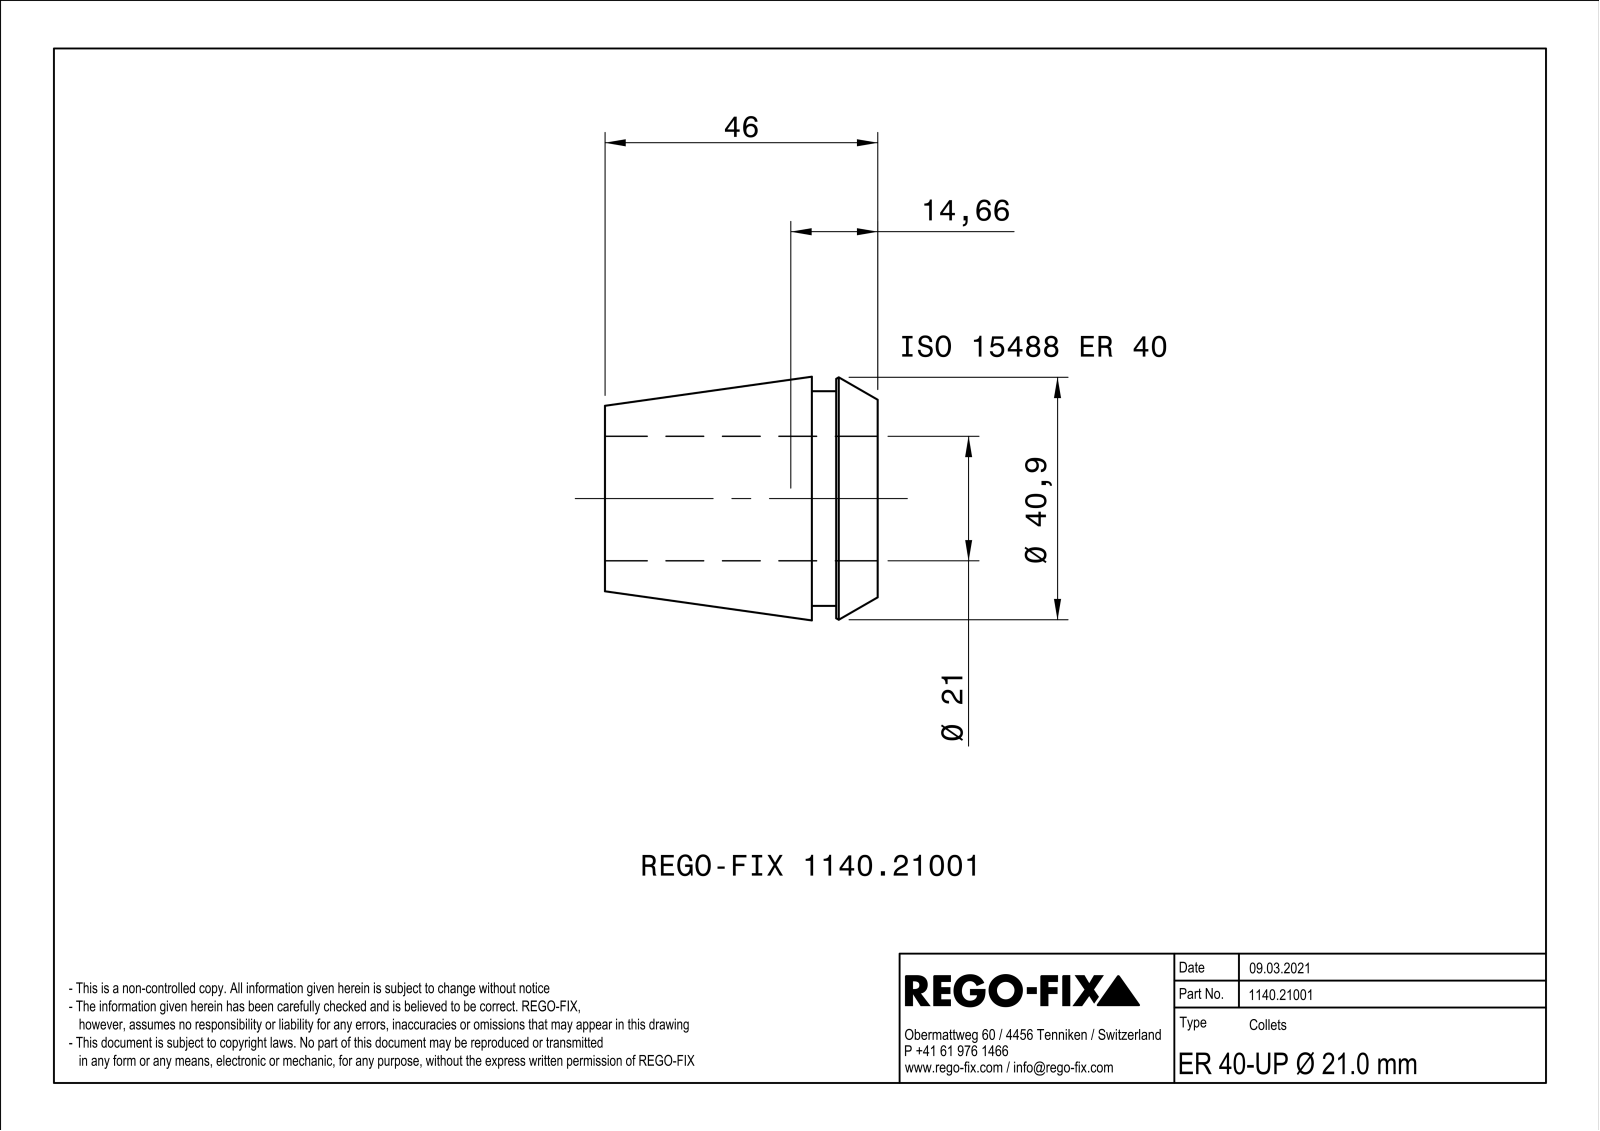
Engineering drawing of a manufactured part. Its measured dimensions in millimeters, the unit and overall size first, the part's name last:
Units: millimetres
Overall size (bounding box): 46 × 40.99 × 40.99
Round holes (diameter × count): ⌀21 ×1
Round bosses / shafts (diameter × count): ⌀36.2 ×1
Main face-to-face distances: 1, 46, 11.1, 34.9, 7, 4.1, 39, 7.5, 0.5, 3.6
Volume: 26 910 mm³ · Surface area: 18 513 mm²
Bodies: 1 solid, 177 faces (88 planar, 9 cylindrical, 80 other)
Part name (STEP PRODUCT): NOCUT
STEP written by: SIEMENS PLM Software Solid Edge ST10 (AUTOMOTIVE_DESIGN)
